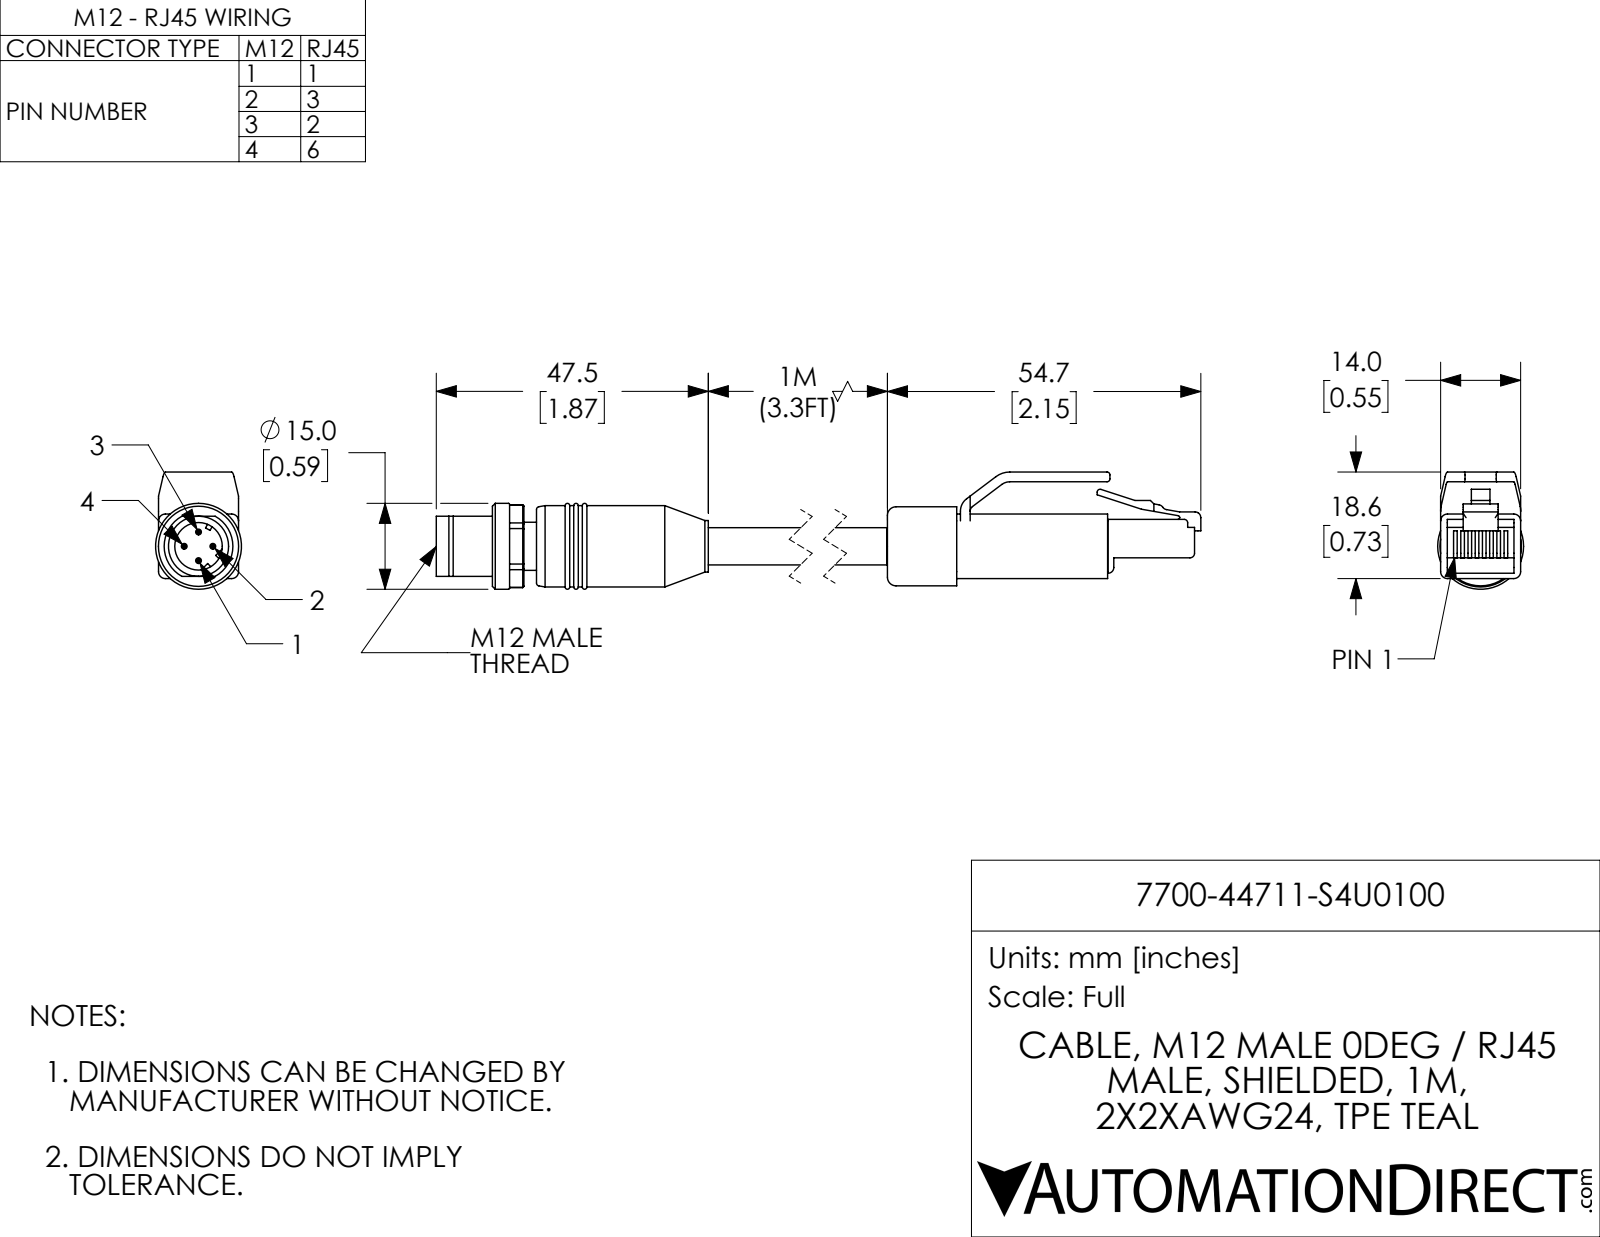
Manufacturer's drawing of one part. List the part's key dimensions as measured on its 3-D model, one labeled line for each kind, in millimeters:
Part name (STEP PRODUCT): 7700-44711-S4U0100_RJ45; 7700-44711-S4U0100; 7700-44711-S4U0100_MALE
STEP written by: SolidWorks 2017 (AUTOMOTIVE_DESIGN)
Units: millimetres
Bodies: 4 solids, 230 faces (121 planar, 67 cylindrical, 42 other)
Overall size (bounding box): 146.3 × 20.5 × 15
Volume: 14 700 mm³ · Surface area: 7 271 mm²
Round holes (diameter × count): ⌀8.3 ×1
Round bosses / shafts (diameter × count): ⌀1 ×4, ⌀15 ×1, ⌀14.2 ×1, ⌀13.8 ×1, ⌀10.5 ×1, ⌀9 ×1, ⌀8.4 ×1, ⌀6.5 ×1
Partial cylindrical surfaces — rounded edges, fillets, slot ends (radius × count): R1.2 ×6, R0.5 ×5, R1 ×5, R0.3 ×2, R0.6 ×1, R0.8 ×1, R2.3 ×1, R2.7 ×1
Main face-to-face distances: 11.3, 14, 1.7, 3.6, 7.6, 10.3, 6.7, 0.9, 16.9, 18.6
